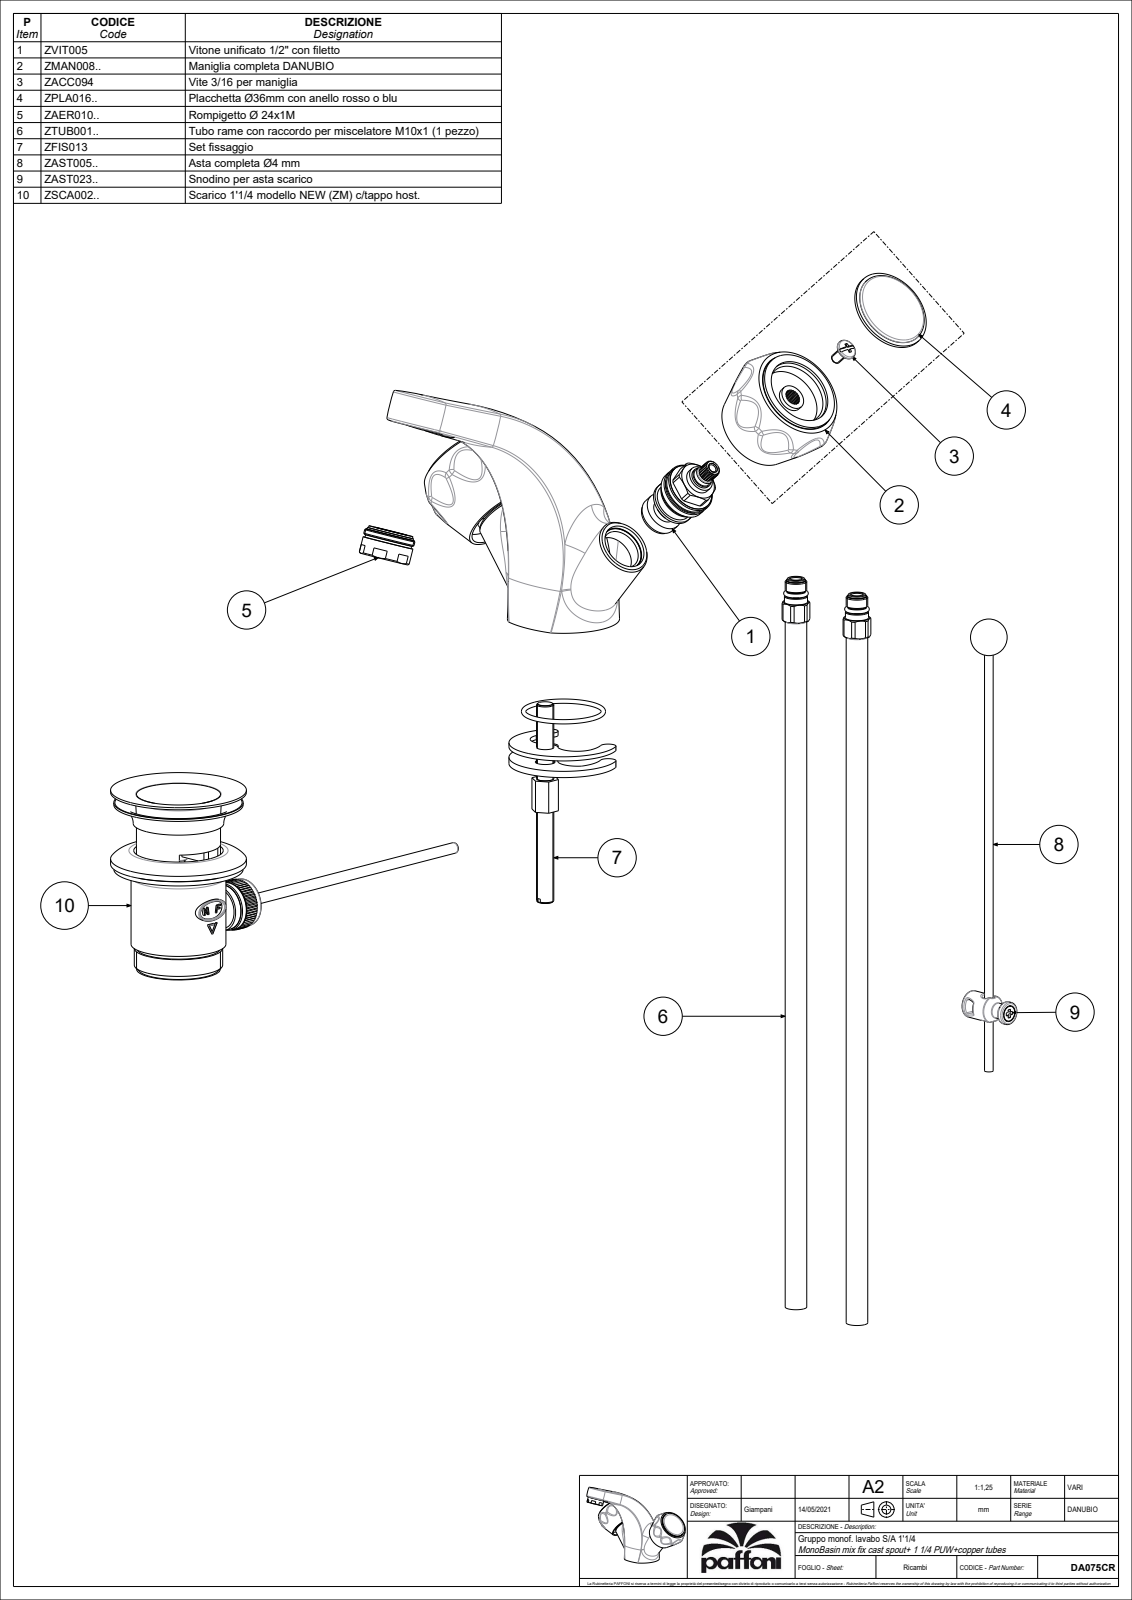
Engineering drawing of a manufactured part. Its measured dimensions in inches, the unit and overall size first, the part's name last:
Units: inches
Overall size (bounding box): 6.265 × 5.298 × 5.053
Round holes (diameter × count): ⌀0.965 ×1
Round bosses / shafts (diameter × count): ⌀1.516 ×2, ⌀0.945 ×1, ⌀0.937 ×1, ⌀0.866 ×1, ⌀0.157 ×1
Partial cylindrical surfaces — rounded edges, fillets, slot ends (radius × count): R0.839 ×16
Main face-to-face distances: 1.39, 0.016, 1.406, 0.902, 0.303, 0.35, 0.047, 0.157, 0.146, 0.193
Volume: 20.34 in³ · Surface area: 65.45 in²
Bodies: 1 solid, 223 faces (22 planar, 30 cylindrical, 171 other)
Part name (STEP PRODUCT): DA075CR
STEP written by: CREO PARAMETRIC BY PTC INC, 2020044 (CONFIG_CONTROL_DESIGN)
